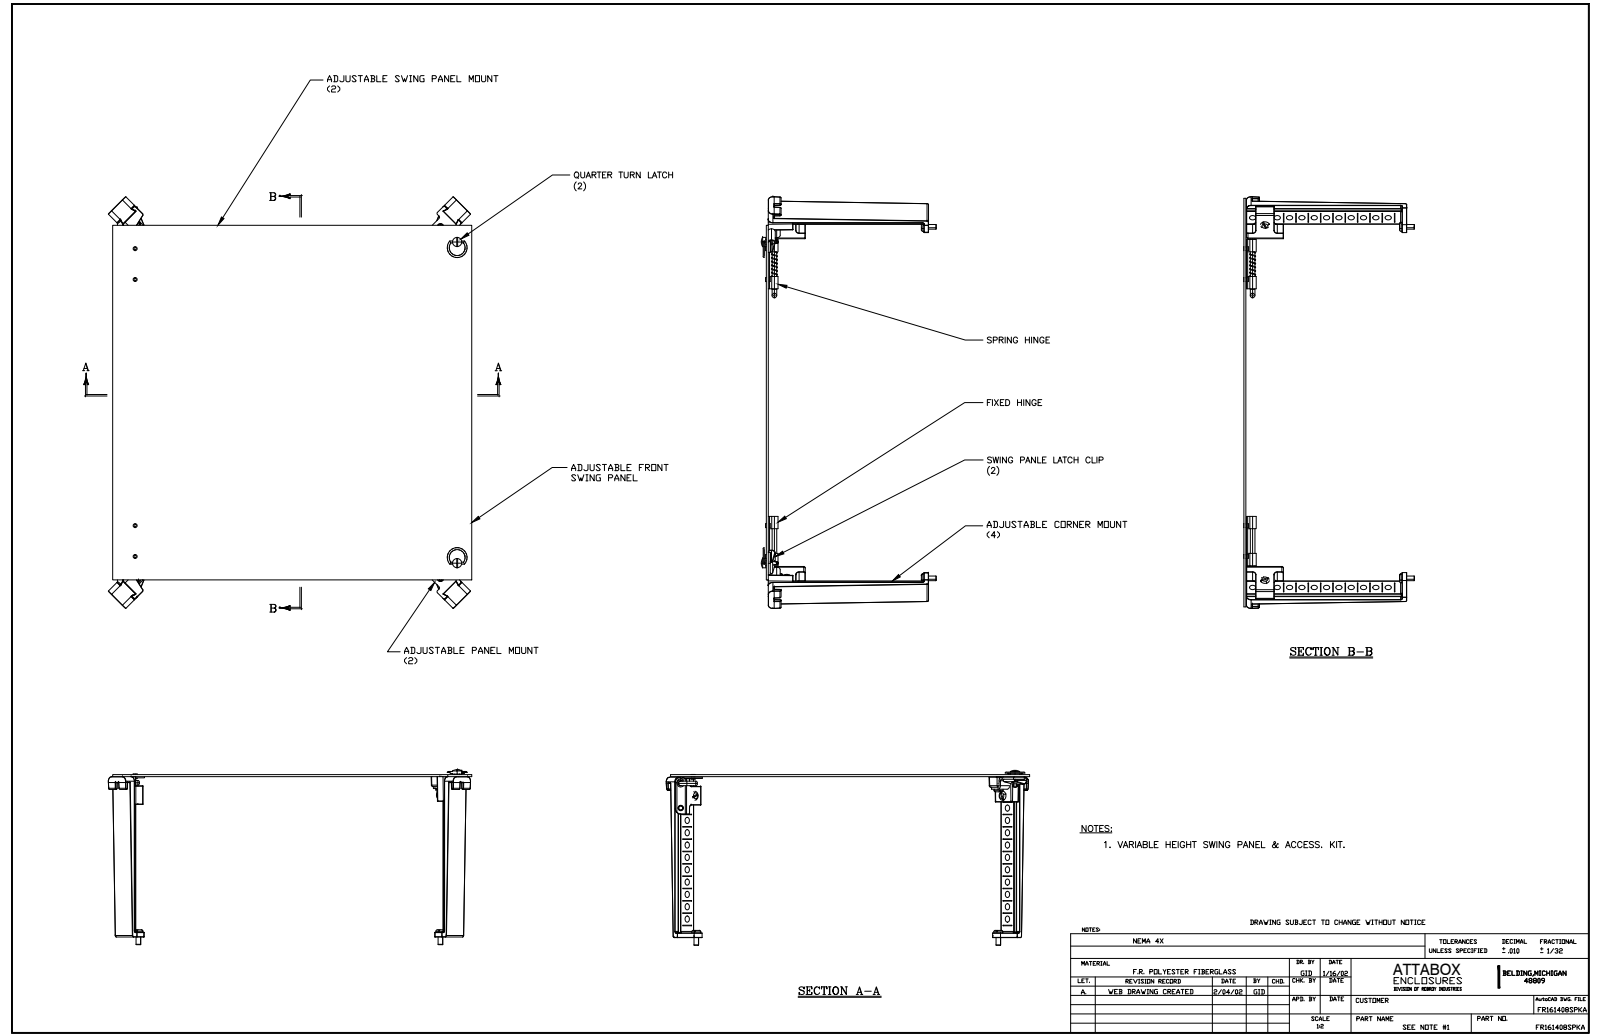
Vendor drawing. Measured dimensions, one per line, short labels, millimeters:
name: FR161408SPKA
written by: SolidWorks 2019 (AUTOMOTIVE_DESIGN)
unit: mm
bodies: 48 solids, 2221 faces (1062 planar, 497 cylindrical, 662 other)
size: 423.9 × 373 × 170.3
volume: 466 400 mm³; area: 376 800 mm²
holes: 52× ⌀6.4, 6× ⌀4, 6× ⌀6.4, 4× ⌀1.3, 4× ⌀3.6, 4× ⌀3.7, 4× ⌀5.5, 4× ⌀5.6, 3× ⌀7.9, 2× ⌀3.9, 2× ⌀5, 2× ⌀8.9
bosses: 10× ⌀4.8, 6× ⌀9.5, 6× ⌀6.2, 4× ⌀11, 4× ⌀8, 4× ⌀4.1, 4× ⌀2, 3× ⌀4.7
rounds: 214× R0.3, 44× R1.5, 10× R1.6, 8× R0.6, 8× R1.6, 8× R3.3, 4× R1.2, 4× R3.2
face distances: 2, 502.4, 5.2, 507.5, 220.5, 281.9, 245.9, 256.5, 25.4, 35.9
hole spacings: 12.7, 38.1, 25.4, 44, 38.1, 52.4, 50.8, 62.2
